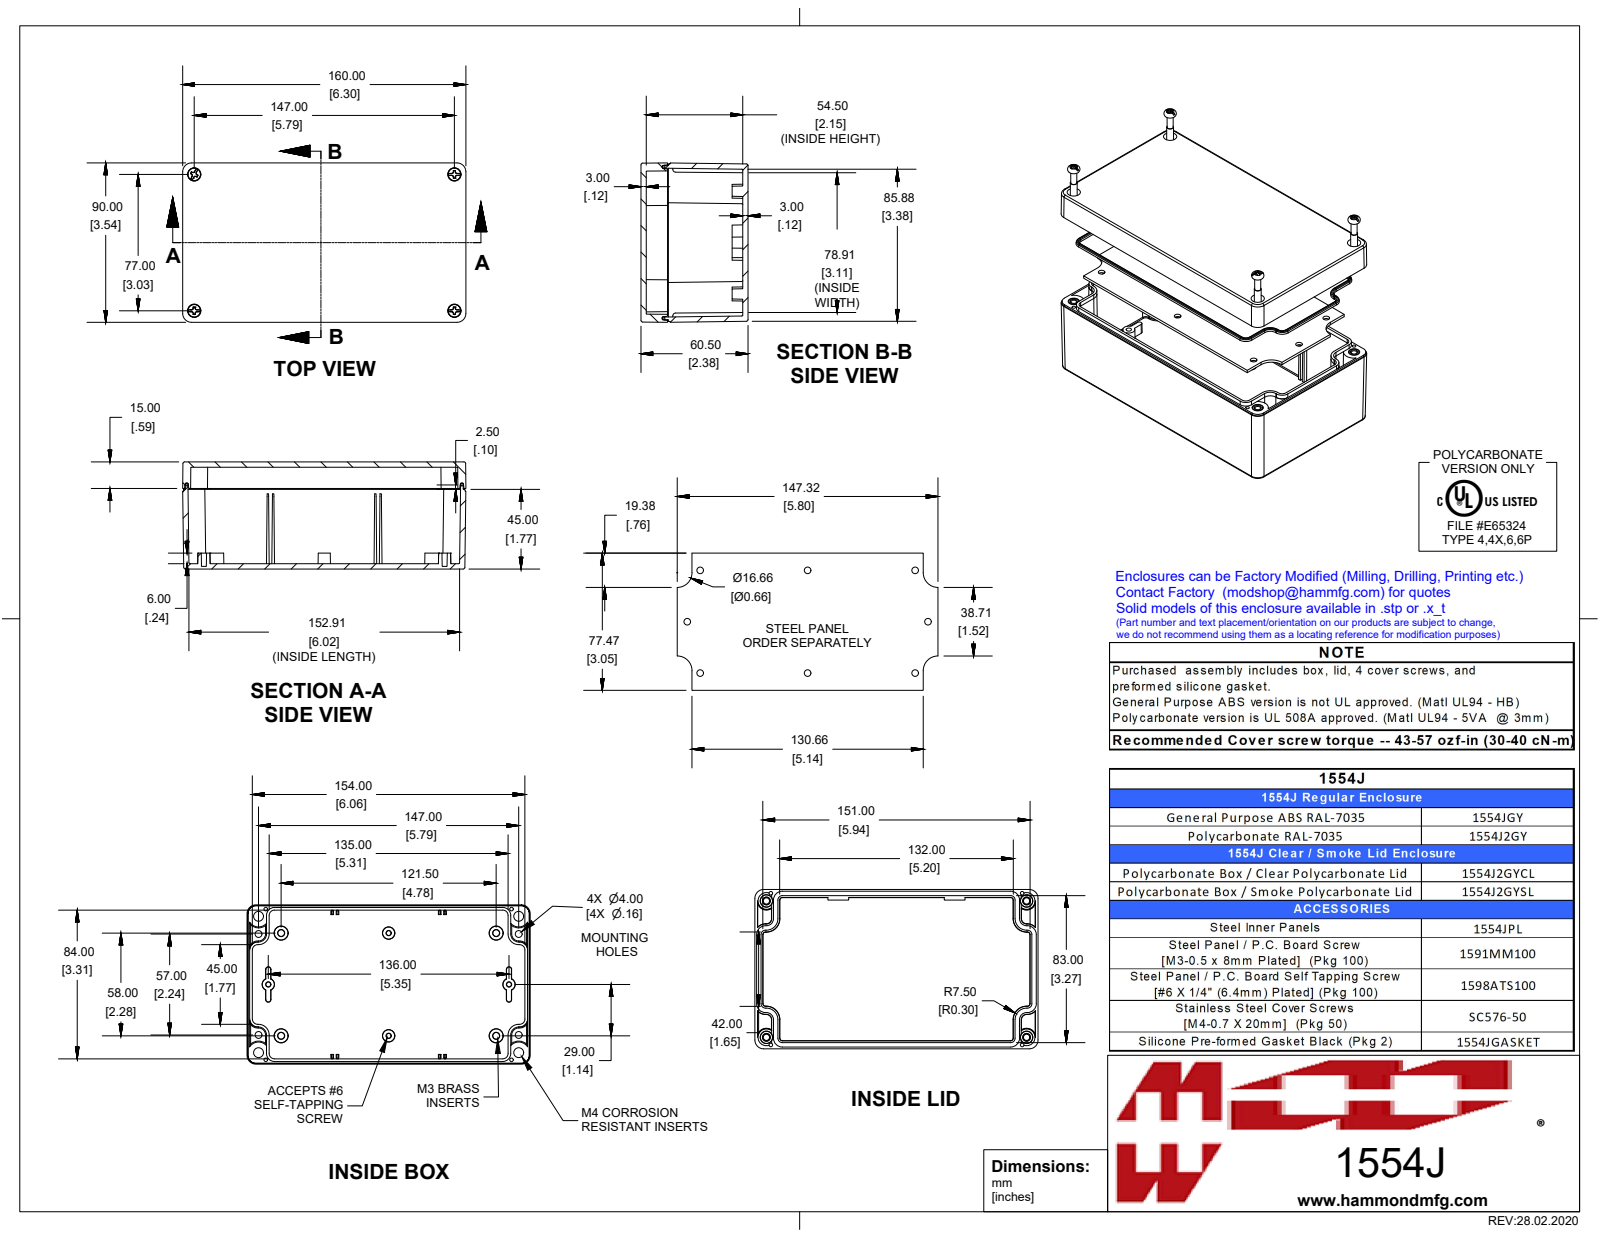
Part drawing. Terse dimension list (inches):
name: 1554J2GY
written by: SolidWorks 2019 (AUTOMOTIVE_DESIGN)
unit: in
bodies: 15 solids, 1318 faces (374 planar, 346 cylindrical, 598 other)
size: 6.299 × 3.543 × 2.382
volume: 11.54 in³; area: 213.7 in²
holes: 8× ⌀0.079, 4× ⌀0.097, 4× ⌀0.128, 4× ⌀0.138, 4× ⌀0.276
bosses: 4× ⌀0.25, 4× ⌀0.218, 4× ⌀0.21, 4× ⌀0.19, 4× ⌀0.154, 4× ⌀0.153, 4× ⌀0.15, 4× ⌀0.135
rounds: 24× R0.02, 12× R0.177, 8× R0.039, 8× R0.118, 8× R0.197, 4× R0.187, 4× R0.236, 3× R0.059
face distances: 0.118, 2.264, 2.382, 2.146, 0.059, 0.177, 0.492, 0.374, 0.079, 0.433
hole spacings: 0.197, 0.626, 0.678, 2.704, 2.857, 3.204, 5.215, 5.299
